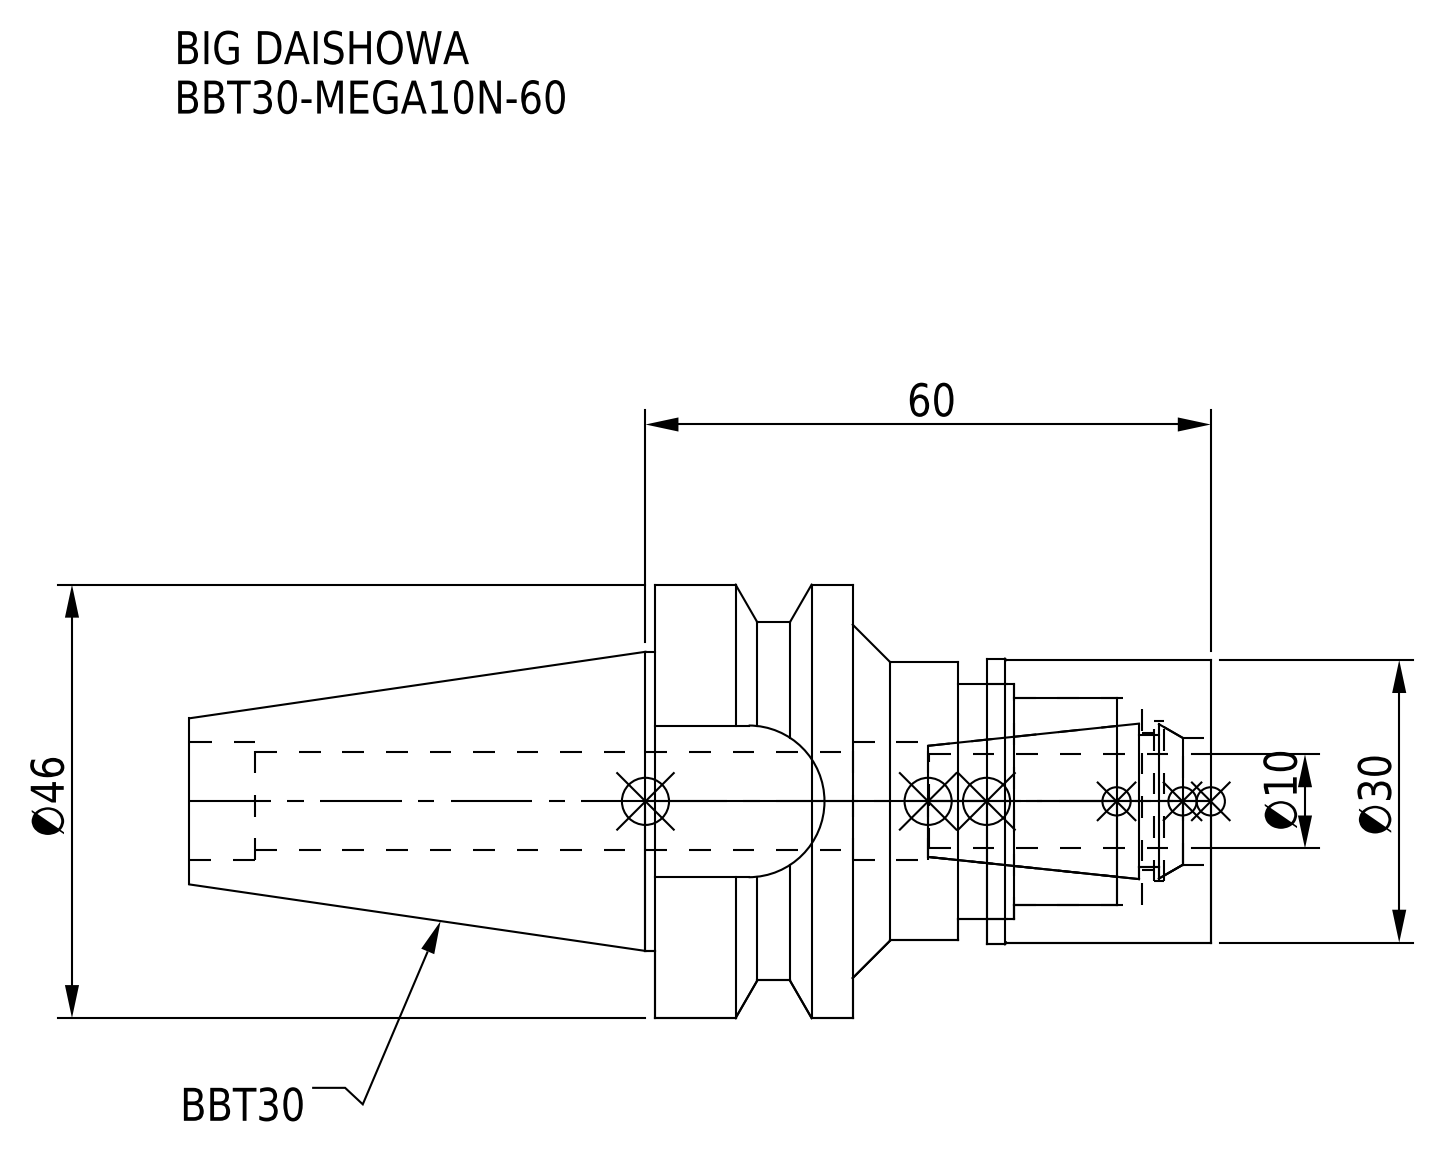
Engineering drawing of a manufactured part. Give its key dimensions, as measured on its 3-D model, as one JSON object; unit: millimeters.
{"part_name": "DXF_TEMP_ASSY_ASM_4_ASM.stp; BBT30-MEGA10N-60-100.stp; BBT30-MEGA10N-60; BBT30-MEGA10N-60_1.stp (+3 more)", "step_written_by": "SolidWorks 2019 (CONFIG_CONTROL_DESIGN)", "units": "millimeters", "bodies": {"solids": 2, "faces": 73, "planar": 21, "cylindrical": 38, "other": 14}, "overall_size": [108.4, 46, 46], "volume_mm3": 68099, "surface_area_mm2": 20569, "round_holes": [[10.4, 1], [12.5, 1], [13.5, 1], [14.5, 1], [17, 1], [22, 1], [25, 1]], "round_bosses_or_shafts": [[46, 1], [31.75, 1], [30.3, 1], [30, 1], [29.5, 1]], "partial_cylinders_radius": [[8.05, 1], [19, 1]], "face_to_face_distances": [21, 38, 59, 32.6, 23.8, 14.2, 35.2, 20.9, 2.9, 17.1]}
